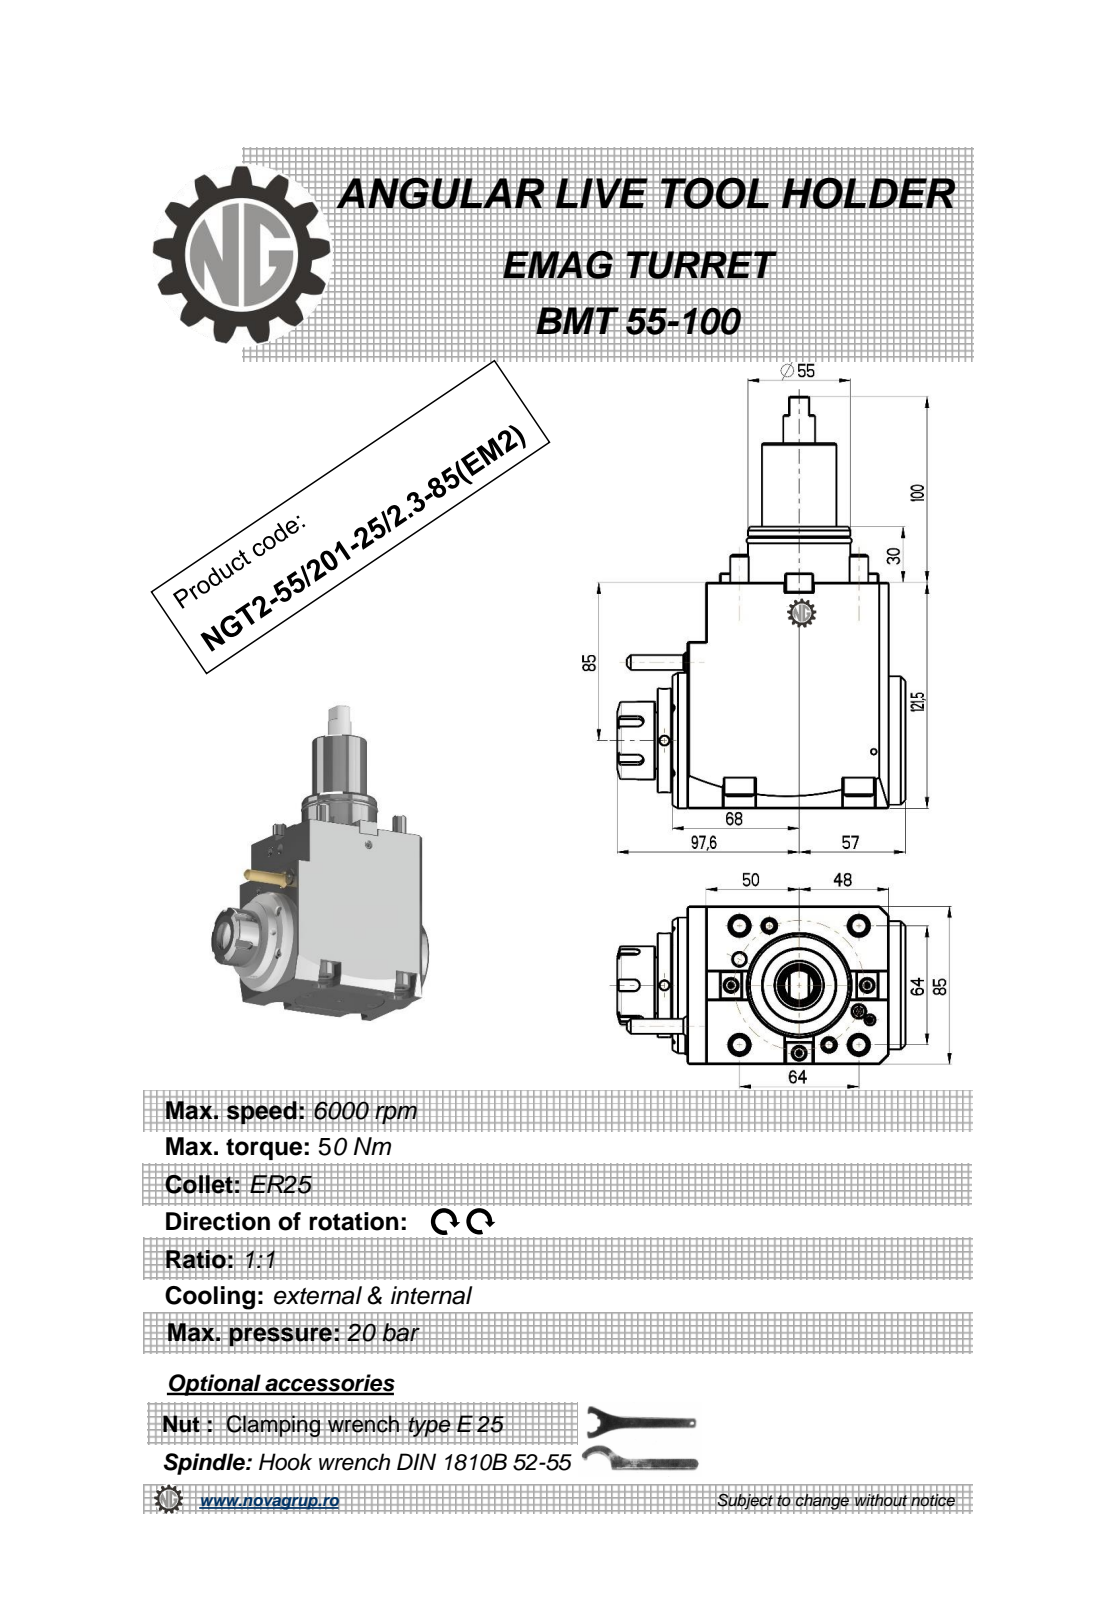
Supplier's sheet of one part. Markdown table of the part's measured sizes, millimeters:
| quantity | value |
| --- | --- |
| part name | NGT2_55_201_25_1_3_85_EM2 |
| STEP written by | PRO/ENGINEER BY PARAMETRIC TECHNOLOGY CORPORATION, 2010280 (CONFIG_CONTROL_DESIGN) |
| units | millimeters |
| bodies | 2 solids, 482 faces (228 planar, 109 cylindrical, 145 other) |
| overall size | 221.5 × 154.6 × 85 |
| volume | 1 308 000 mm³ |
| surface area | 112 900 mm² |
| round holes (diameter × count) | 5 × 3, 6.8 × 2, 3 × 1, 12 × 1 |
| round bosses / shafts (diameter × count) | 16 × 4, 10 × 4, 73 × 1, 69 × 1, 56 × 1, 55 × 1, 50 × 1, 43.4 × 1 |
| partial cylindrical surfaces (radius × count) | 0.32 × 20, 0.22 × 6, 3 × 5, 8.5 × 4, 0.8 × 2, 480 × 2 |
| main face-to-face distances | 85, 121.5, 8, 9, 107, 10, 108, 117, 98, 18 |
| hole center spacings | 42.62, 69.86, 105.19 |
